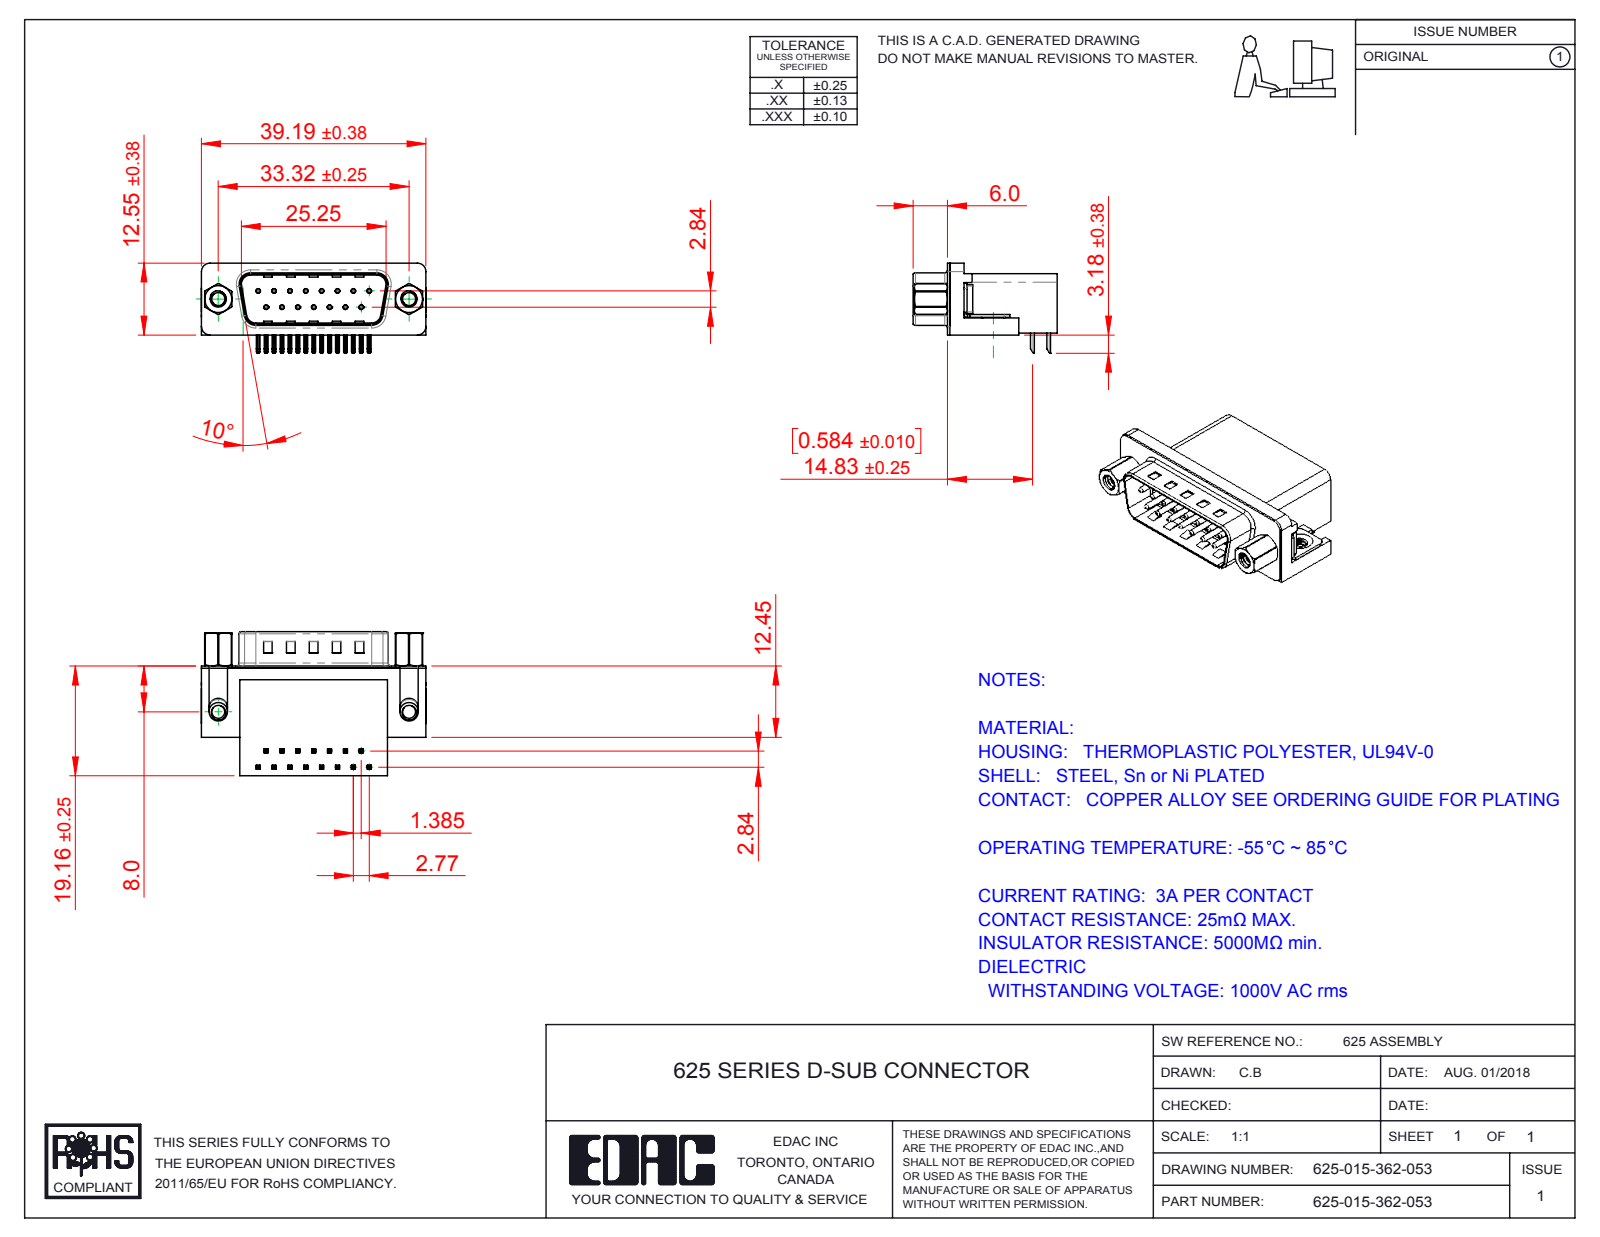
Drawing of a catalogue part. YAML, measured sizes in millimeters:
part_name: "625 Housing_15 Socket; 625 Contact Bottom; 625 4-40 Threaded Board Mount; 625 Shell_15 Socket (+4 more)"
step_written_by: "SolidWorks 2016 (CONFIG_CONTROL_DESIGN)"
units: millimeters
bodies: {solids: 23, faces: 1637, planar: 917, cylindrical: 531, other: 189}
overall_size: [39.22, 25.16, 15.73]
volume: 6467
surface_area: 6987
round_holes:
  - {diameter: 0.35, count: 15}
  - {diameter: 0.8, count: 15}
  - {diameter: 2.26, count: 4}
  - {diameter: 2.29, count: 2}
  - {diameter: 4, count: 2}
  - {diameter: 4.8, count: 2}
  - {diameter: 5, count: 2}
round_bosses_or_shafts:
  - {diameter: 0.75, count: 15}
  - {diameter: 4.9, count: 2}
  - {diameter: 4.75, count: 2}
  - {diameter: 3.9, count: 2}
  - {diameter: 3.26, count: 2}
  - {diameter: 2.79, count: 2}
partial_cylinders:
  - {radius: 0.25, count: 68}
  - {radius: 0.12, count: 30}
  - {radius: 1, count: 16}
  - {radius: 0.5, count: 9}
  - {radius: 1.6, count: 8}
  - {radius: 1.5, count: 6}
  - {radius: 0.9, count: 4}
  - {radius: 2, count: 4}
face_to_face_distances: [0.4, 10.35, 18.76, 2.1, 19.16, 10.46, 1.7, 10.86, 8.76, 16.26]
hole_center_spacings: [3.16, 2.77, 5.54, 8.31, 11.08, 5.03, 5.04, 7.48]
